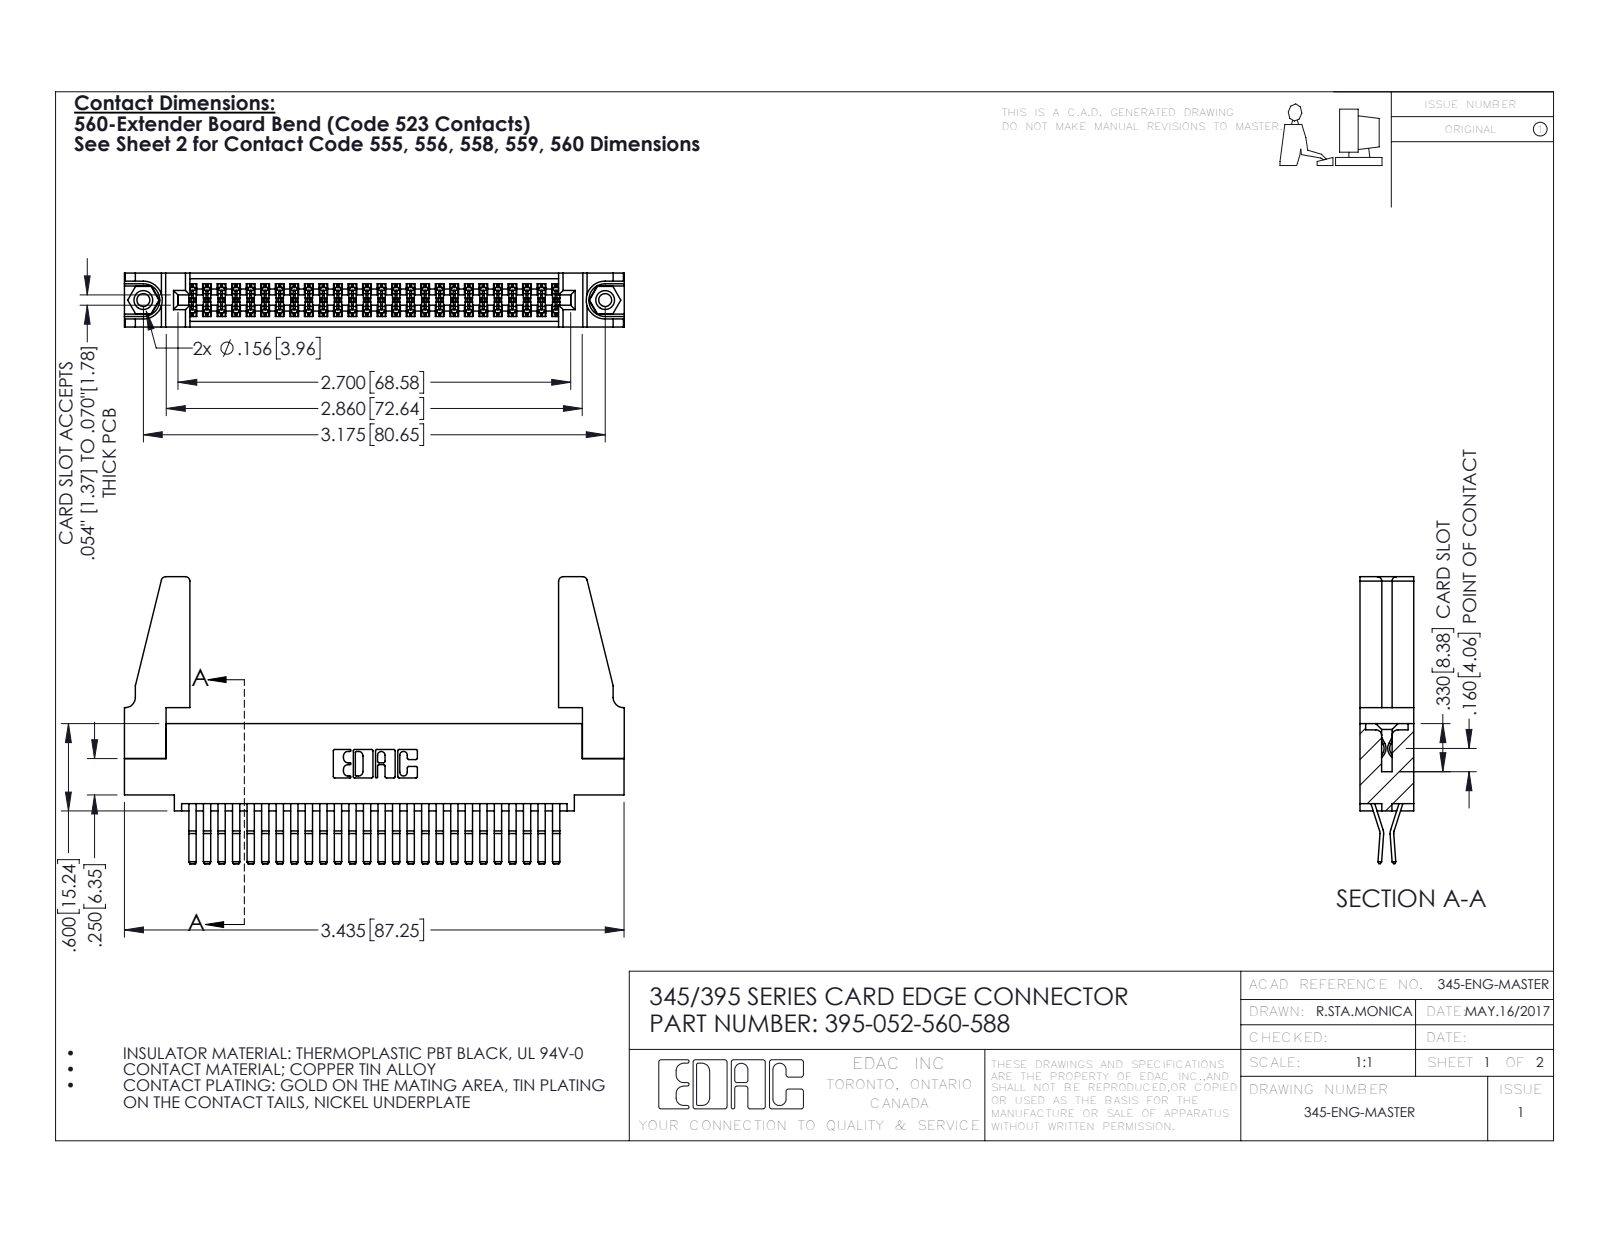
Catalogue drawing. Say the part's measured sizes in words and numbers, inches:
The part is named "345-220-078_345-220-088; 345-250-001_345-250-001-102; 395-052-560-588; 345 Part_0.110 Offset - 0.156 Dia-TH (+1 more)". Its 3-D file was written by "SolidWorks 2016 (CONFIG_CONTROL_DESIGN)". It is 57 solids with 2958 faces: 1872 planar, 1070 cylindrical and 16 other. Overall it measures 3.436 by 1.972 by 0.37 inches. Its volume is 0.723 cubic inches and its surface area 25.56 square inches. Round holes: 2 of diameter 0.089, 2 of diameter 0.125, 2 of diameter 0.156, 1 of diameter 0.064. Round bosses or shafts: 2 of diameter 0.155. Partial cylindrical surfaces (rounded edges, fillets, slot ends): 79 of radius 0.006, 22 of radius 0.01, 8 of radius 0.03, 6 of radius 0.007, 6 of radius 0.031, 3 of radius 0.026, 2 of radius 0.01, 2 of radius 0.014. The main face-to-face distances are 0.072, 0.298, 0.37, 0.025, 0.2, 0.098, 0.272, 0.225, 0.175, 0.149. The hole center spacings are 0.27, 2.94, 3.175.
